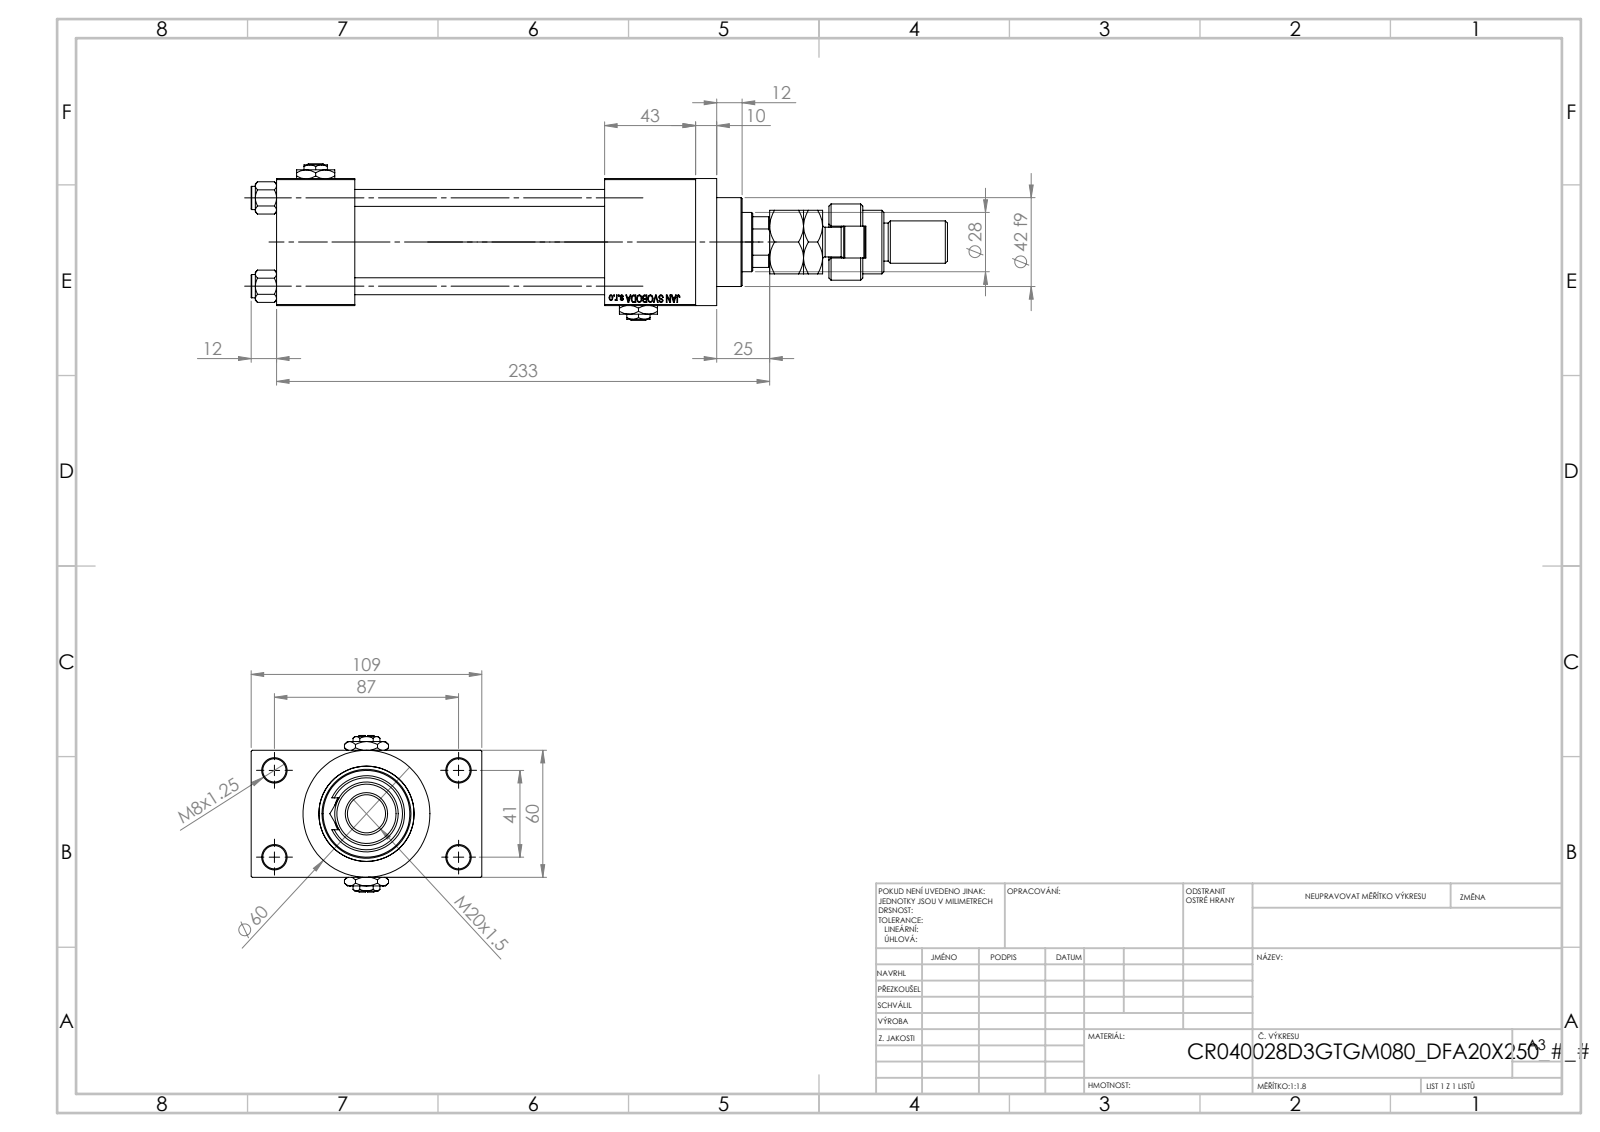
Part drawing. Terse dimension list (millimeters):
name: V215CR_D_Body; NUT_M5_D; V215_VC_A; V215CR_VCP_D (+4 more)
written by: SolidWorks 2019 (CONFIG_CONTROL_DESIGN)
unit: mm
bodies: 15 solids, 1274 faces (570 planar, 102 cylindrical, 602 other)
size: 329 × 109 × 74
volume: 659 252 mm³; area: 170 401 mm²
holes: 4× ⌀8, 4× ⌀11, 2× ⌀7, 2× ⌀16.66, 2× ⌀24, 1× ⌀18.5, 1× ⌀28, 1× ⌀31, 1× ⌀40, 1× ⌀45
bosses: 4× ⌀11, 1× ⌀60, 1× ⌀46, 1× ⌀42, 1× ⌀36, 1× ⌀30, 1× ⌀22, 1× ⌀20
rounds: 1× R7.5, 1× R12, 1× R13.5
face distances: 60, 24.5, 84.5, 118, 37, 155, 43, 198, 161, 109
hole spacings: 22.65, 29.49, 41.7, 47.15, 48.09, 64.35, 76.49, 41
